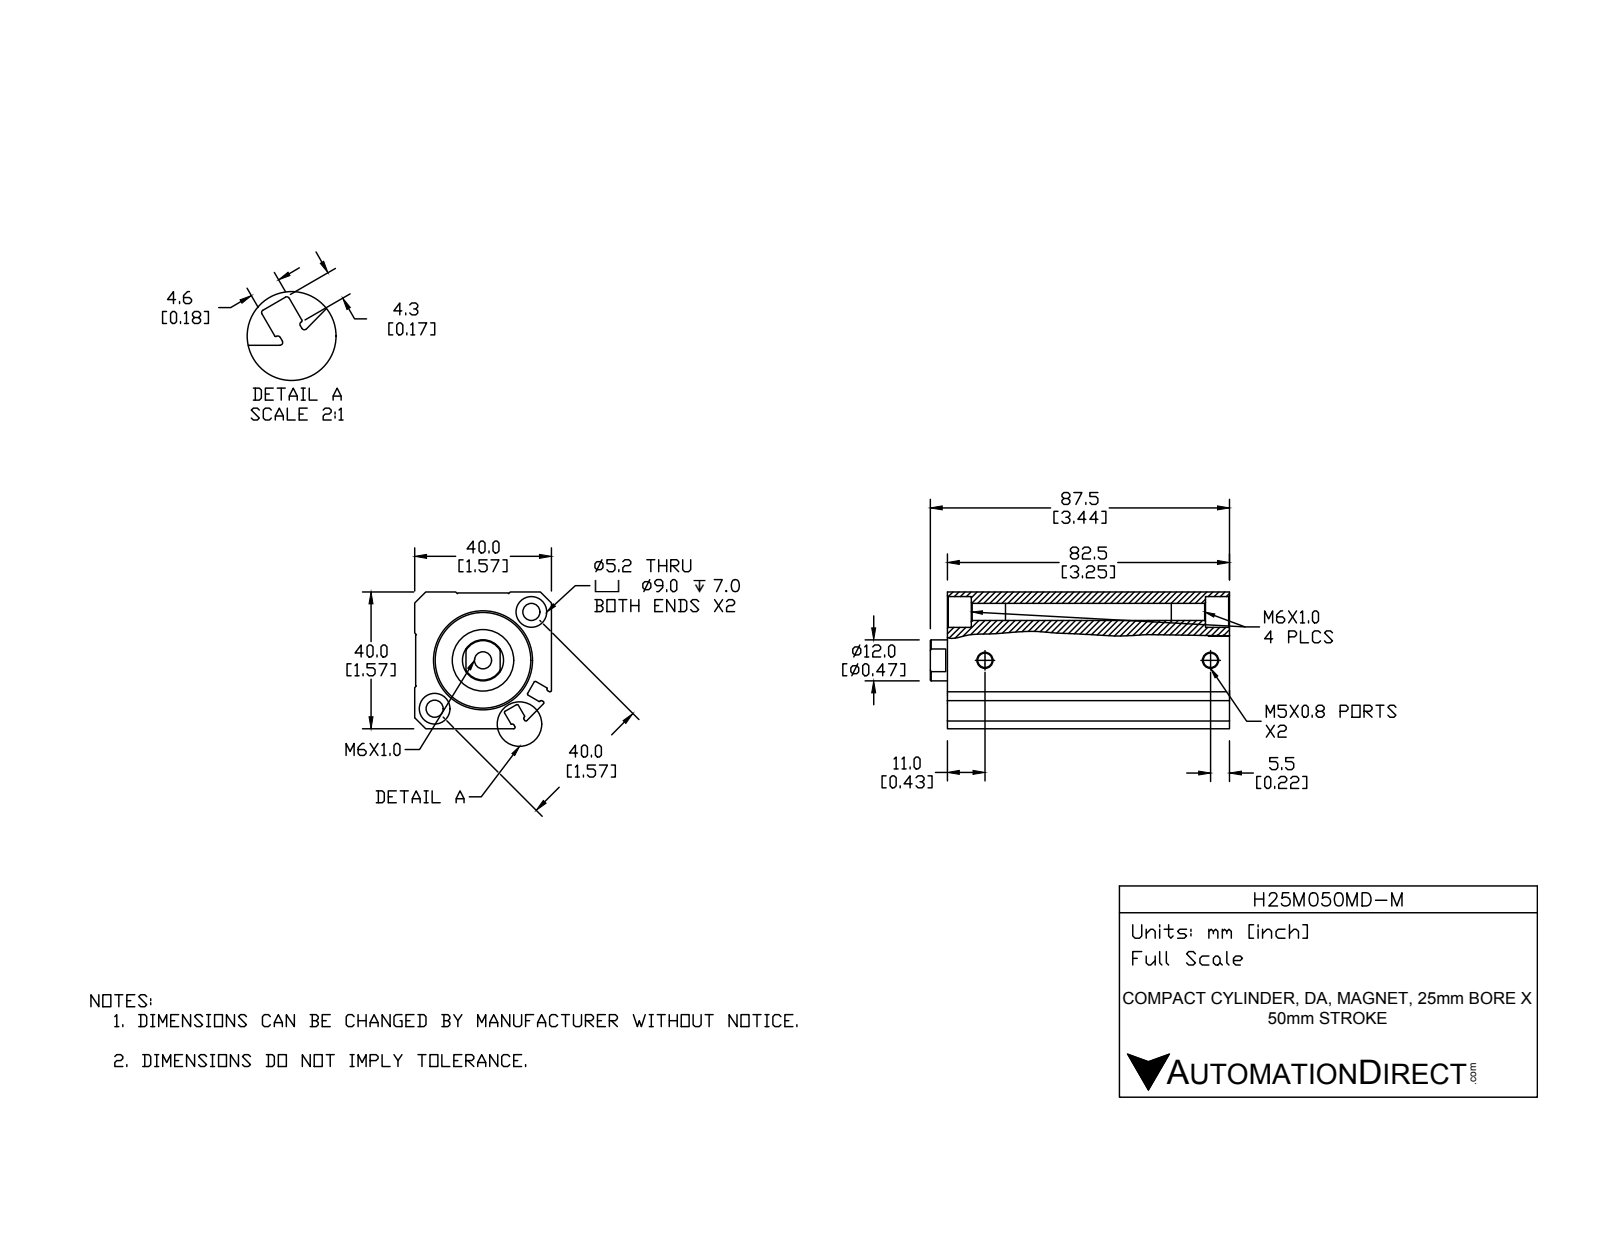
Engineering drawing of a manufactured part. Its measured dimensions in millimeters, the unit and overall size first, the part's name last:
Units: millimetres
Overall size (bounding box): 87.5 × 40 × 40
Round holes (diameter × count): ⌀5 ×3, ⌀4.2 ×2, ⌀9 ×2, ⌀12 ×1, ⌀16 ×1, ⌀25 ×1, ⌀28 ×1
Round bosses / shafts (diameter × count): ⌀18 ×1, ⌀14 ×1
Partial cylindrical surfaces — rounded edges, fillets, slot ends (radius × count): R0.4 ×12, R0.2 ×4
Main face-to-face distances: 40, 39.7, 4, 82.5, 78.5, 4.6, 1.4, 2.6, 81.1, 71.5
Hole centre spacings: 20, 39.99, 66
Volume: 96 373 mm³ · Surface area: 32 289 mm²
Bodies: 2 solids, 141 faces (53 planar, 55 cylindrical, 33 other)
Part name (STEP PRODUCT): H25M050MD-M; H25M050MD-M-BODY; H25M050MD-M-PISTON
STEP written by: SolidWorks 2015 (CONFIG_CONTROL_DESIGN)
